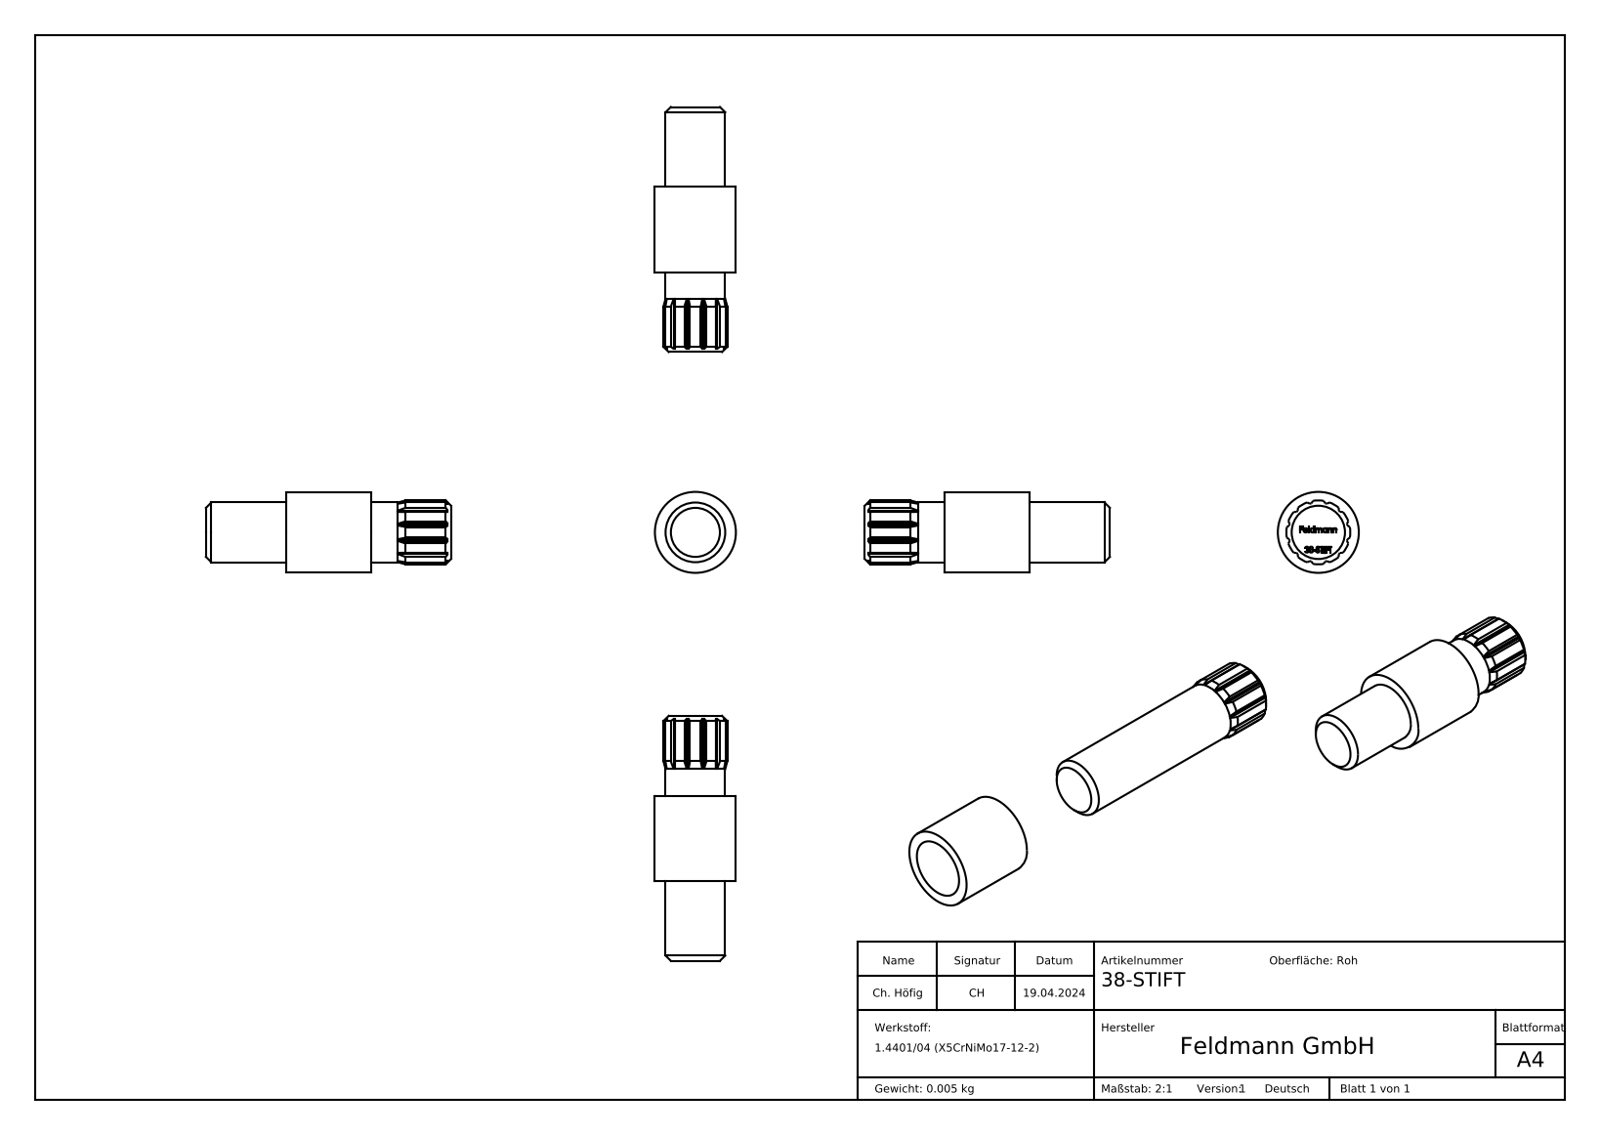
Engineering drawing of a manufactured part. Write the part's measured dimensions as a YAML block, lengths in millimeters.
part_name: "38-STIFT Teil1_38-STIFT Teil1; 38-STIFT; 38-STIFT Teil2"
step_written_by: "SolidWorks 2018 (CONFIG_CONTROL_DESIGN)"
units: millimeters
bodies: {solids: 2, faces: 265, planar: 142, cylindrical: 15, other: 108}
overall_size: [23, 7.6, 7.6]
volume: 741
surface_area: 836
round_holes:
  - {diameter: 5.6, count: 1}
round_bosses_or_shafts:
  - {diameter: 7.6, count: 1}
partial_cylinders:
  - {radius: 3, count: 1}
face_to_face_distances: [7.5, 15.5, 8, 23, 4.04, 4.02, 7.4, 15.4, 22.9, 1.35]
